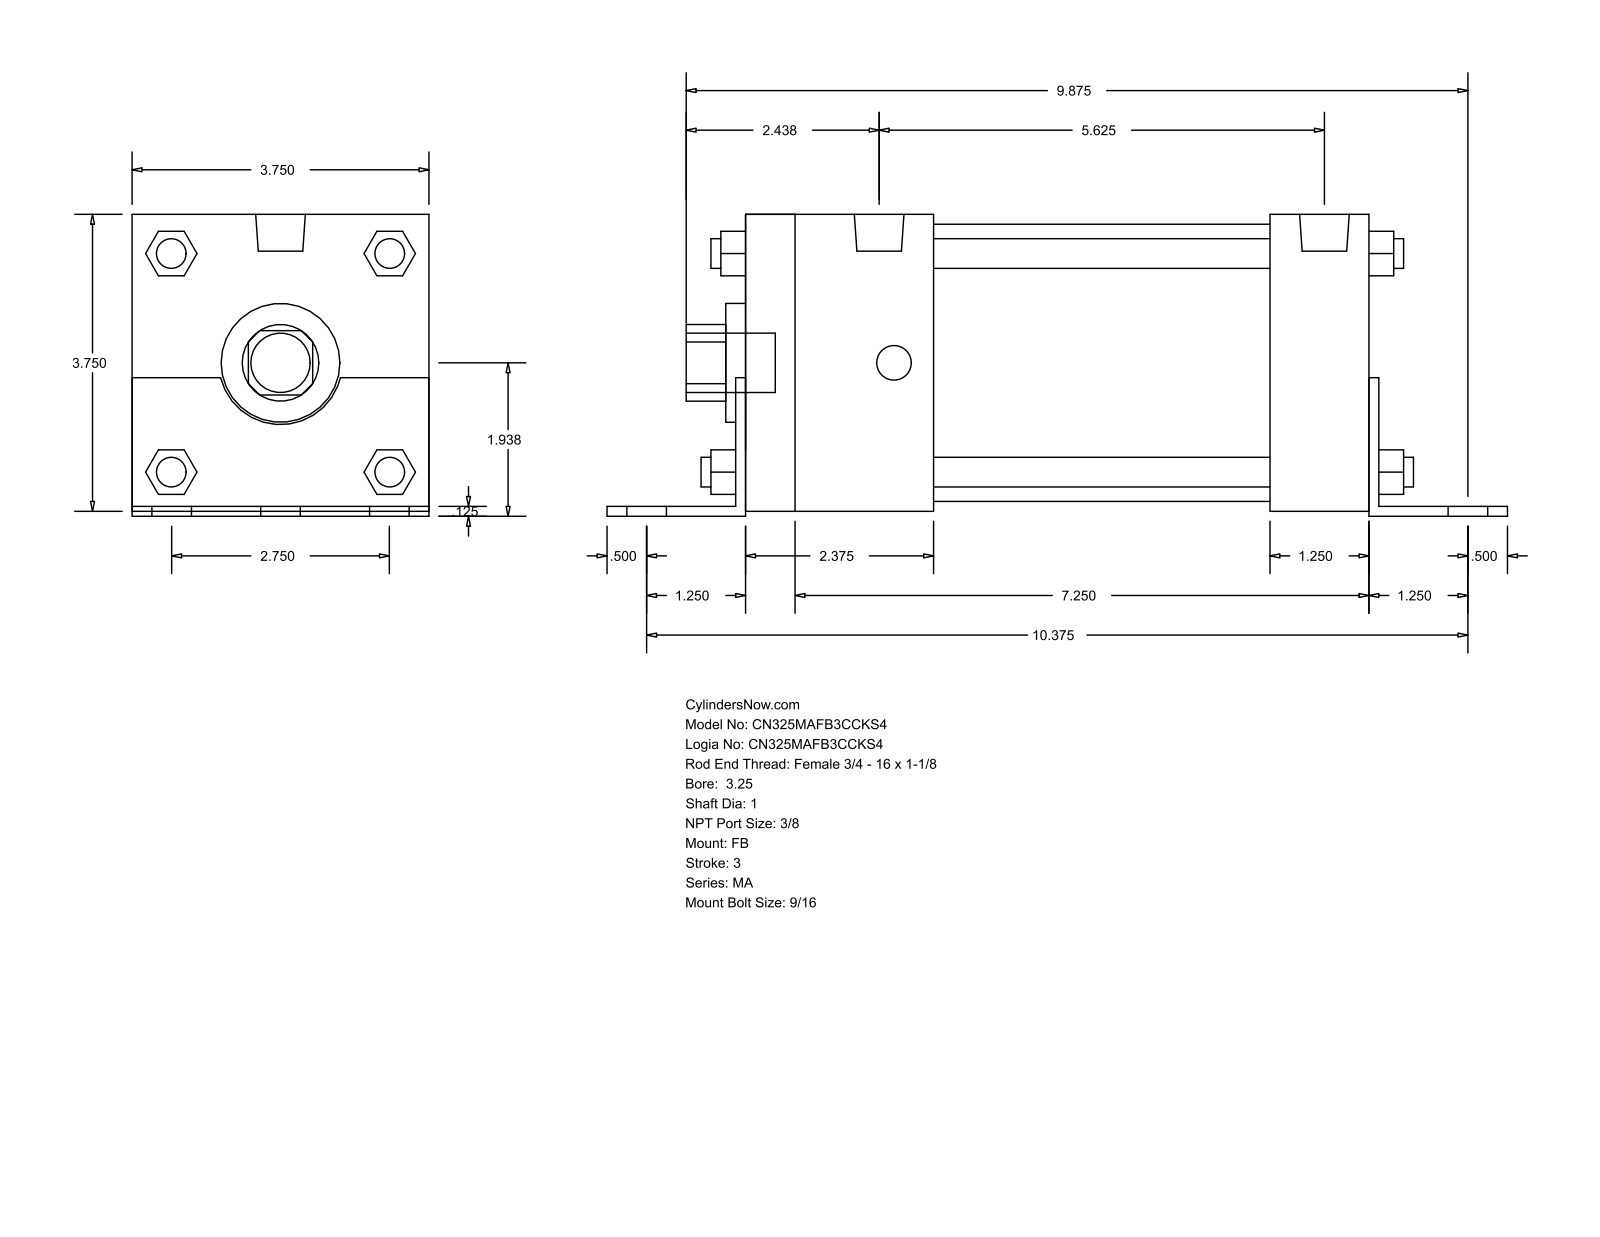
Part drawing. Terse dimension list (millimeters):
name: MA_FB__0325_1
written by: GSSL Pune (CONFIG_CONTROL_DESIGN)
unit: mm
bodies: 0 solids, 140 faces (105 planar, 35 cylindrical, 0 other)
size: 288.93 × 96.84 × 95.25
holes: 1× ⌀25.4, 1× ⌀38.1, 1× ⌀88.9
bosses: 6× ⌀14.29, 4× ⌀11.11, 4× ⌀9.53, 2× ⌀15.93, 1× ⌀19.05
rounds: 1× R12.29, 1× R19.81
face distances: 95.24, 3.17, 1.59, 96.83, 1.58, 93.66, 3.18, 200.02, 206.37, 203.2
